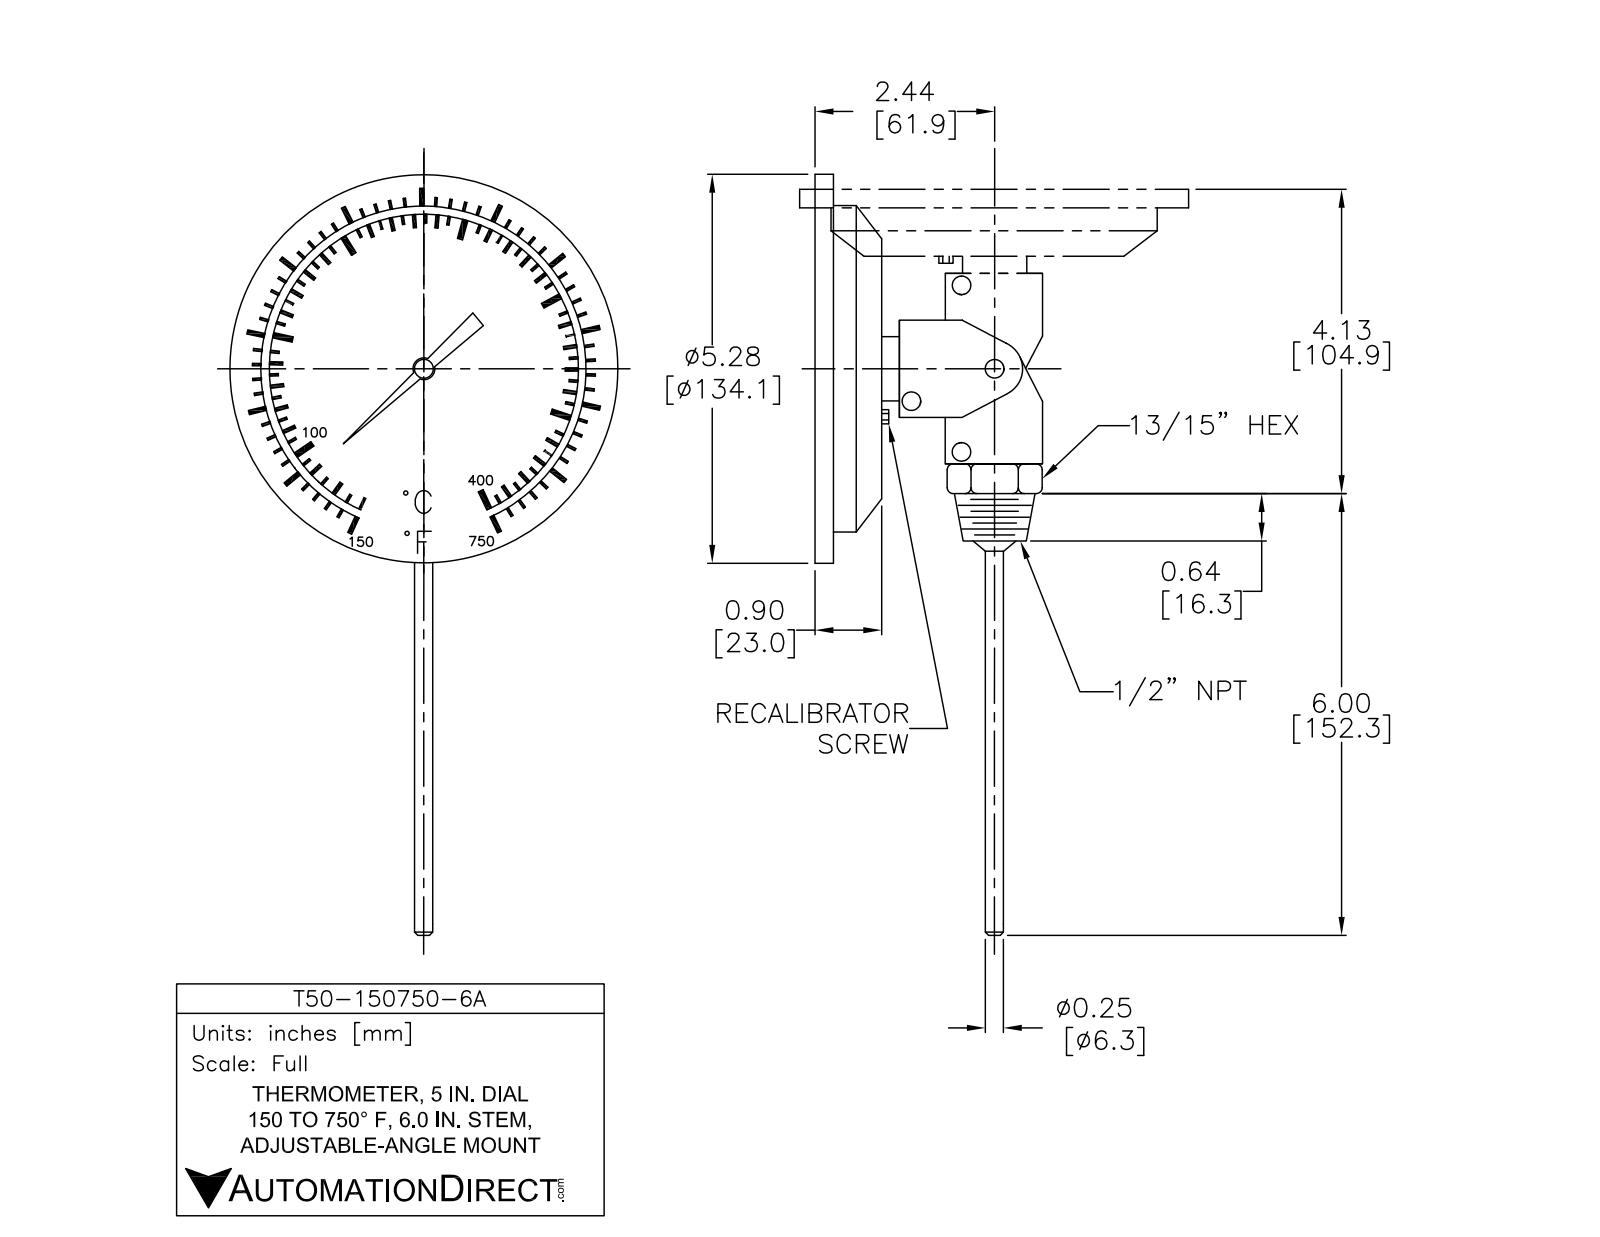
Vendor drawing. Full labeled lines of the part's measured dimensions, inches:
Part name (STEP PRODUCT): T50-150750-6A
STEP written by: SolidWorks 2021 (AUTOMOTIVE_DESIGN)
Units: inches
Bodies: 1 solid, 499 faces (296 planar, 45 cylindrical, 158 other)
Overall size (bounding box): 9.96 × 5.28 × 5.28
Volume: 10.23 in³ · Surface area: 98.36 in²
Round holes (diameter × count): ⌀3.424 ×1, ⌀3.706 ×1, ⌀4.76 ×1, ⌀4.836 ×1
Round bosses / shafts (diameter × count): ⌀0.305 ×4, ⌀0.145 ×2, ⌀5.28 ×1, ⌀4.97 ×1, ⌀3.454 ×1, ⌀0.85 ×1, ⌀0.821 ×1, ⌀0.544 ×1
Partial cylindrical surfaces — rounded edges, fillets, slot ends (radius × count): R0.06 ×10, R0.04 ×4, R0.17 ×1, R0.336 ×1, R0.336 ×1, R0.342 ×1, R0.4 ×1, R1.868 ×1
Main face-to-face distances: 0.353, 0.074, 0.055, 0.427, 1.19, 0.815, 0.462, 0.388, 1.245, 2.435
